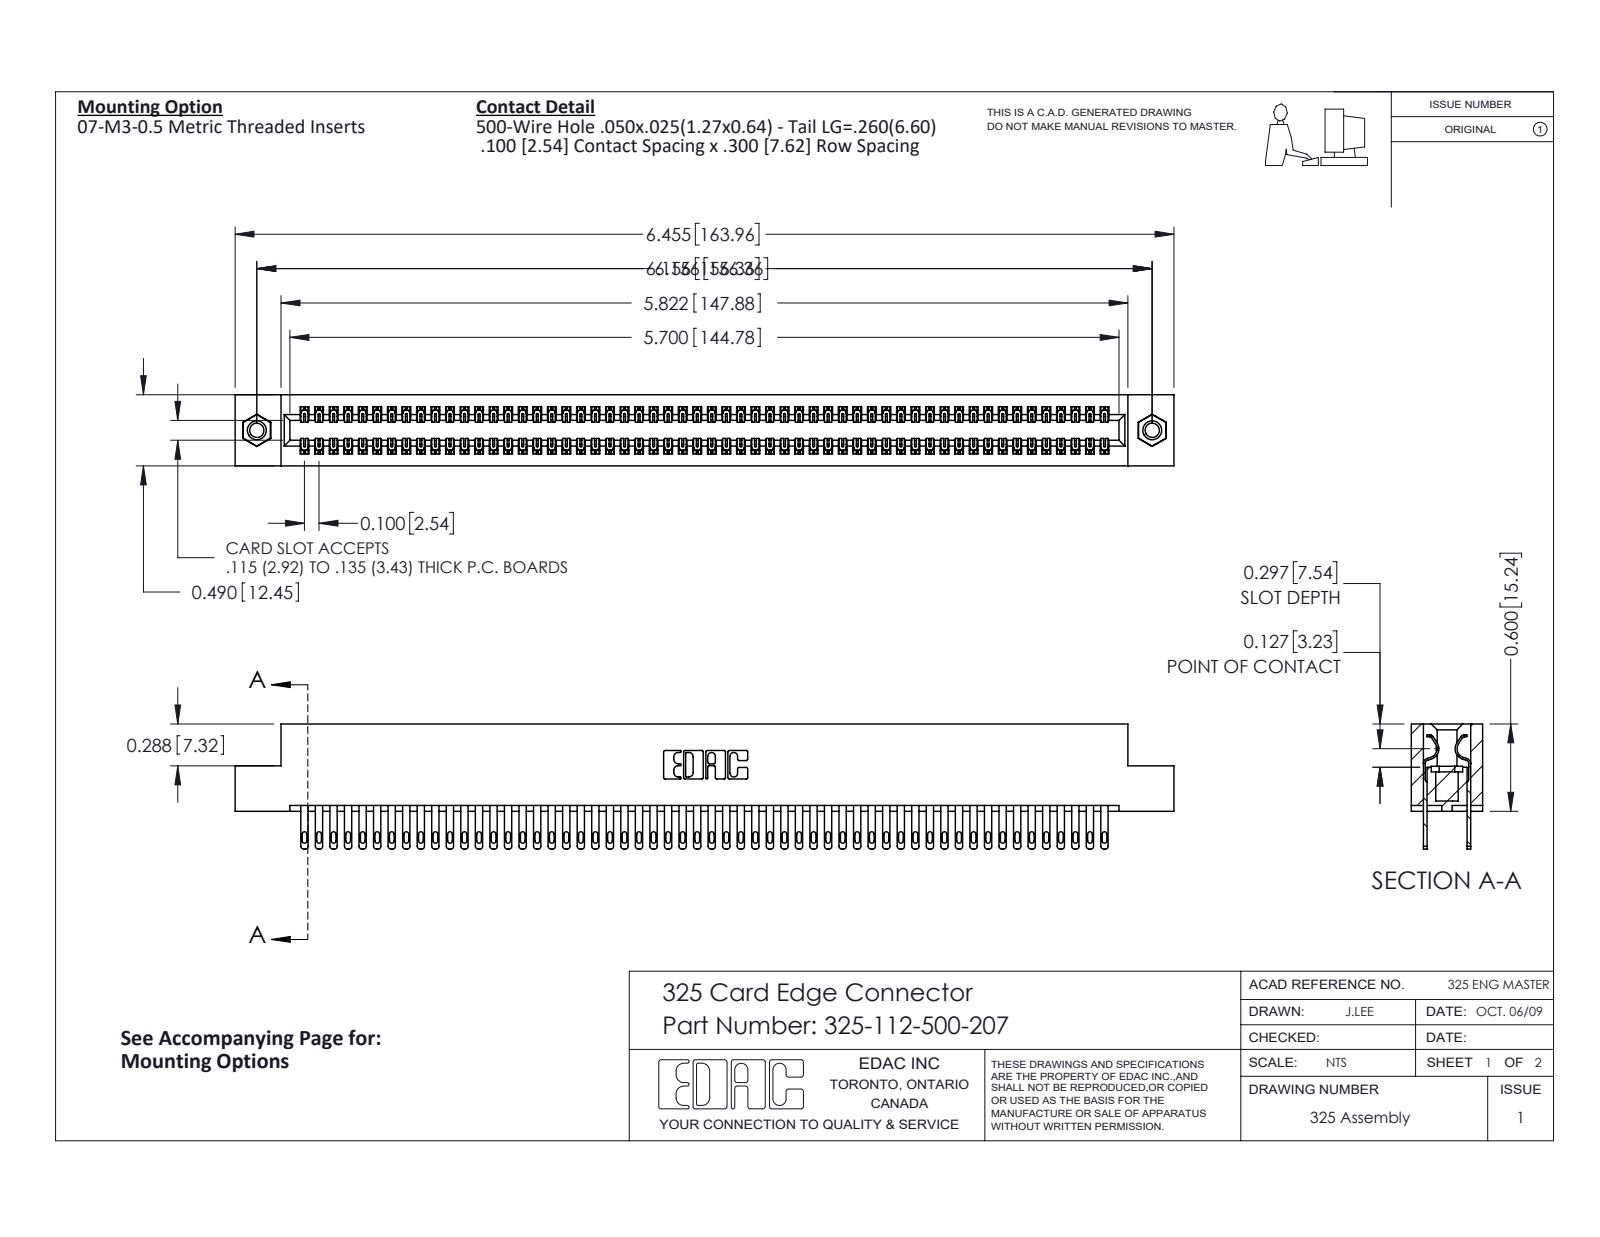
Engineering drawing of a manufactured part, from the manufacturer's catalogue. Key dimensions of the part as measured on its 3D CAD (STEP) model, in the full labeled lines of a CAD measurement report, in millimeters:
Part name (STEP PRODUCT): 325-112-500-207; 325 Part_TI; 325-292-001_325-293-100; 345-250-001_345-250-005-103
STEP written by: SolidWorks 2016 (CONFIG_CONTROL_DESIGN)
Units: millimetres
Bodies: 115 solids, 5550 faces (3462 planar, 2072 cylindrical, 16 other)
Overall size (bounding box): 164 × 21.8 × 12.4
Volume: 21 610 mm³ · Surface area: 27 700 mm²
Round holes (diameter × count): ⌀2.5 ×2, ⌀3.2 ×2, ⌀4.1 ×2
Round bosses / shafts (diameter × count): ⌀3.9 ×2
Partial cylindrical surfaces — rounded edges, fillets, slot ends (radius × count): R0.2 ×168, R0.4 ×112, R0.5 ×112, R0.3 ×22, R0.2 ×6, R0.8 ×6, R0.7 ×3, R0.4 ×2
Main face-to-face distances: 2.1, 10.3, 7.6, 2.7, 9.7, 0.6, 12.4, 8.3, 7, 6.7
Hole centre spacings: 156.4
